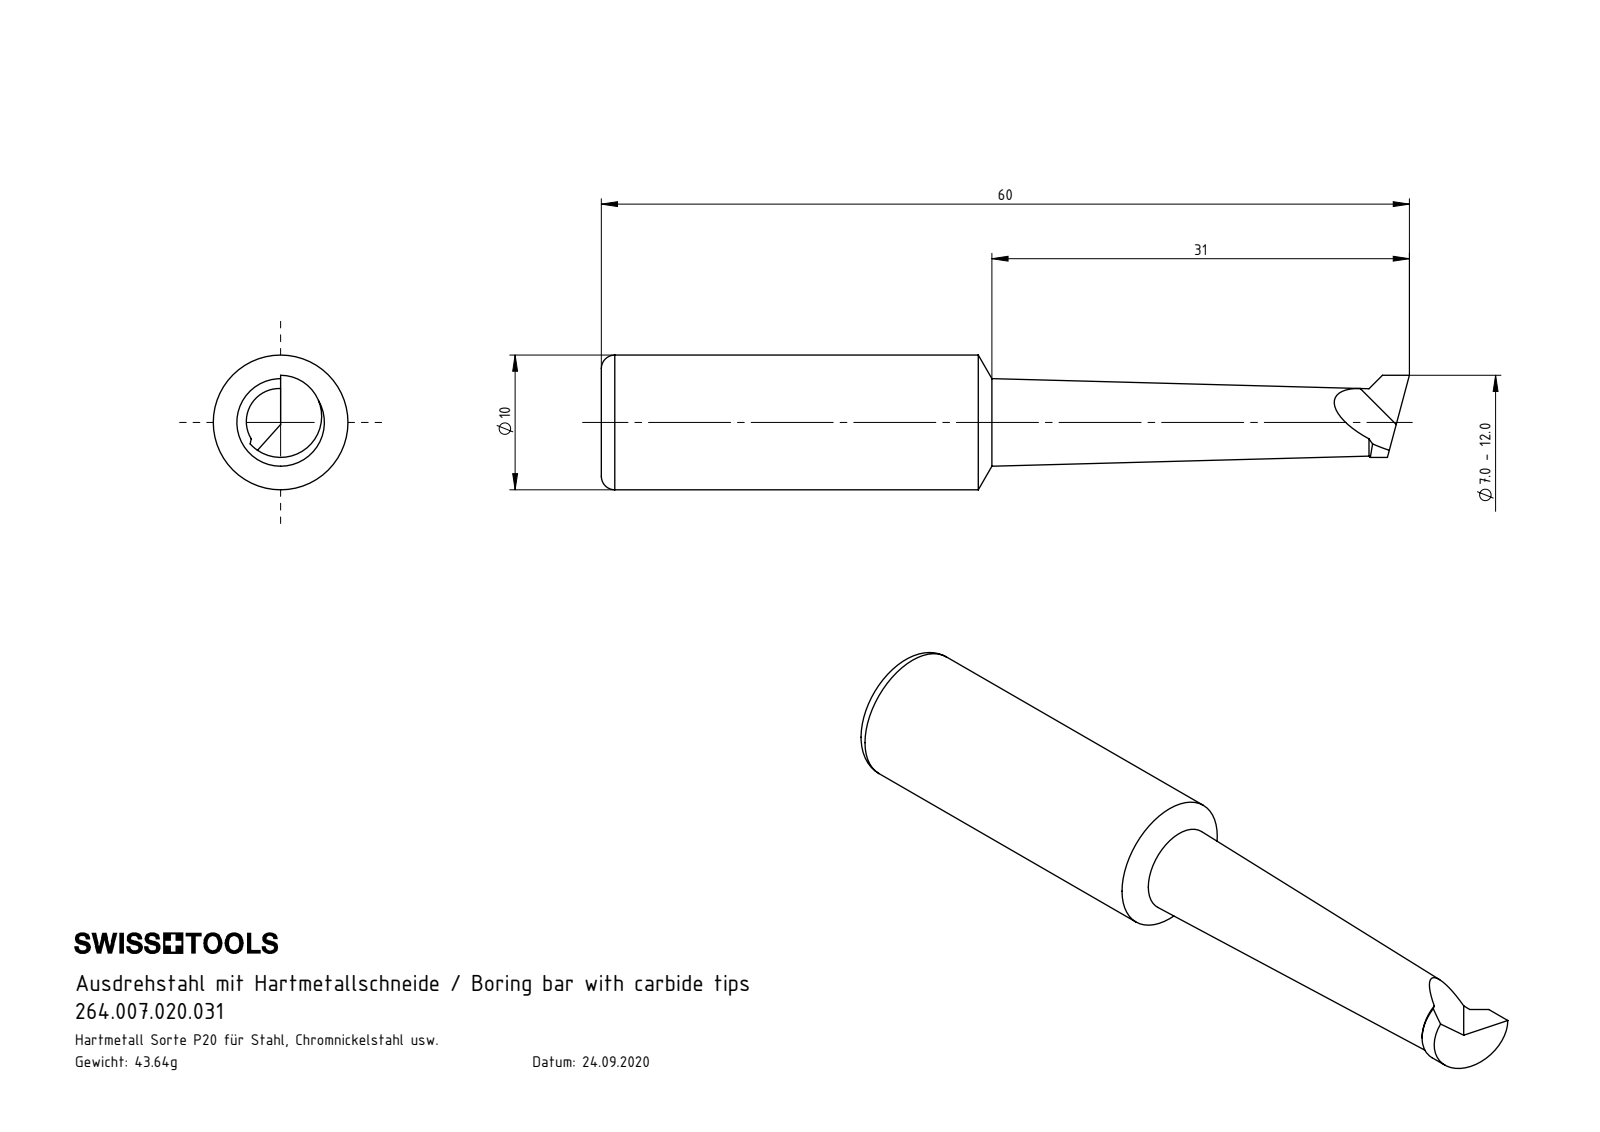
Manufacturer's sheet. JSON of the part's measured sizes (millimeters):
{"part_name": "U10.B07.001.031", "step_written_by": "SolidWorks 2017 (AUTOMOTIVE_DESIGN)", "units": "millimeters", "bodies": {"solids": 1, "faces": 10, "planar": 4, "cylindrical": 2, "other": 4}, "overall_size": [60, 10, 10], "volume_mm3": 3010, "surface_area_mm2": 1559, "round_bosses_or_shafts": [[10, 1]], "partial_cylinders_radius": [[3.05, 1]]}
